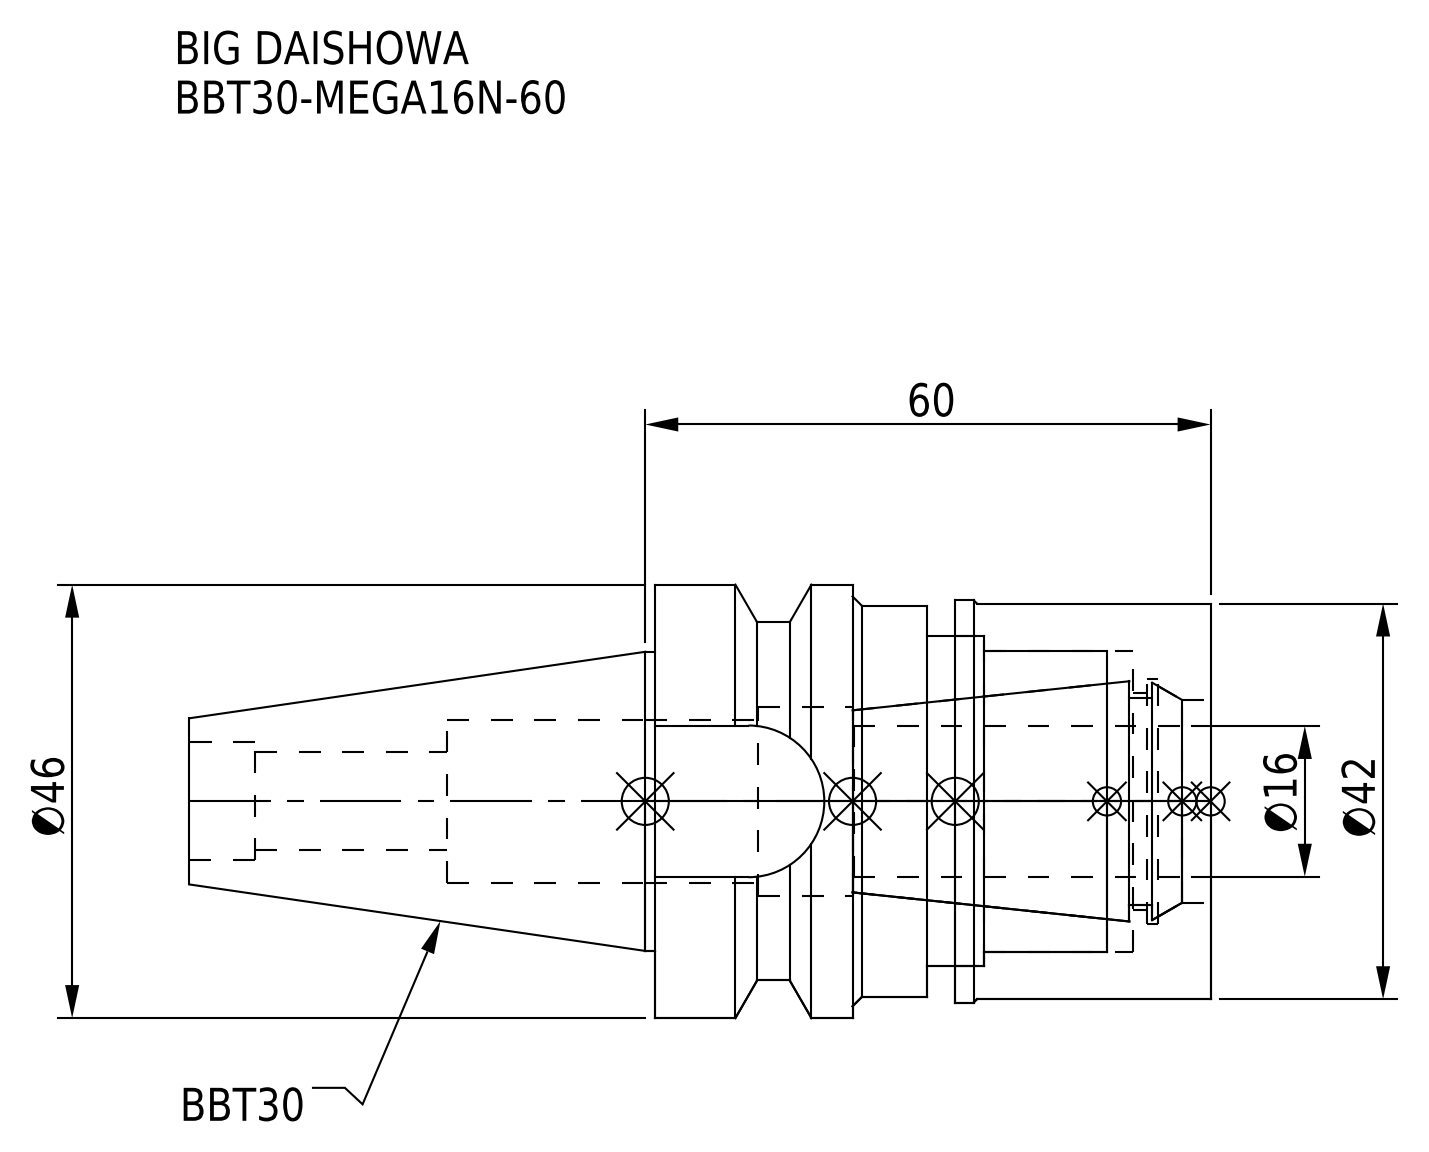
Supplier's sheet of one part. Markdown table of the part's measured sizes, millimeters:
| quantity | value |
| --- | --- |
| part name | BBT30MN16060-160_ASM.stp; MGN16_1.stp; BBT30-MEGA16N-60-160-FreeParts; BBT30-MEGA16N-60-160.stp (+3 more) |
| STEP written by | SolidWorks 2019 (CONFIG_CONTROL_DESIGN) |
| units | millimeters |
| bodies | 2 solids, 76 faces (22 planar, 40 cylindrical, 14 other) |
| overall size | 108.4 × 46 × 46 |
| volume | 75 508 mm³ |
| surface area | 26 452 mm² |
| round holes (diameter × count) | 10.4 × 1, 12.5 × 1, 17.3 × 1, 20 × 1, 21.5 × 1, 23 × 1, 26 × 1, 32 × 1, 35 × 1 |
| round bosses / shafts (diameter × count) | 46 × 1, 42.7 × 1, 42 × 1, 41.5 × 1, 31.75 × 1 |
| partial cylindrical surfaces (radius × count) | 8.05 × 1, 19 × 1 |
| main face-to-face distances | 59, 27.1, 31.9, 16.1, 24, 11, 48, 30.1, 3, 28.9 |
